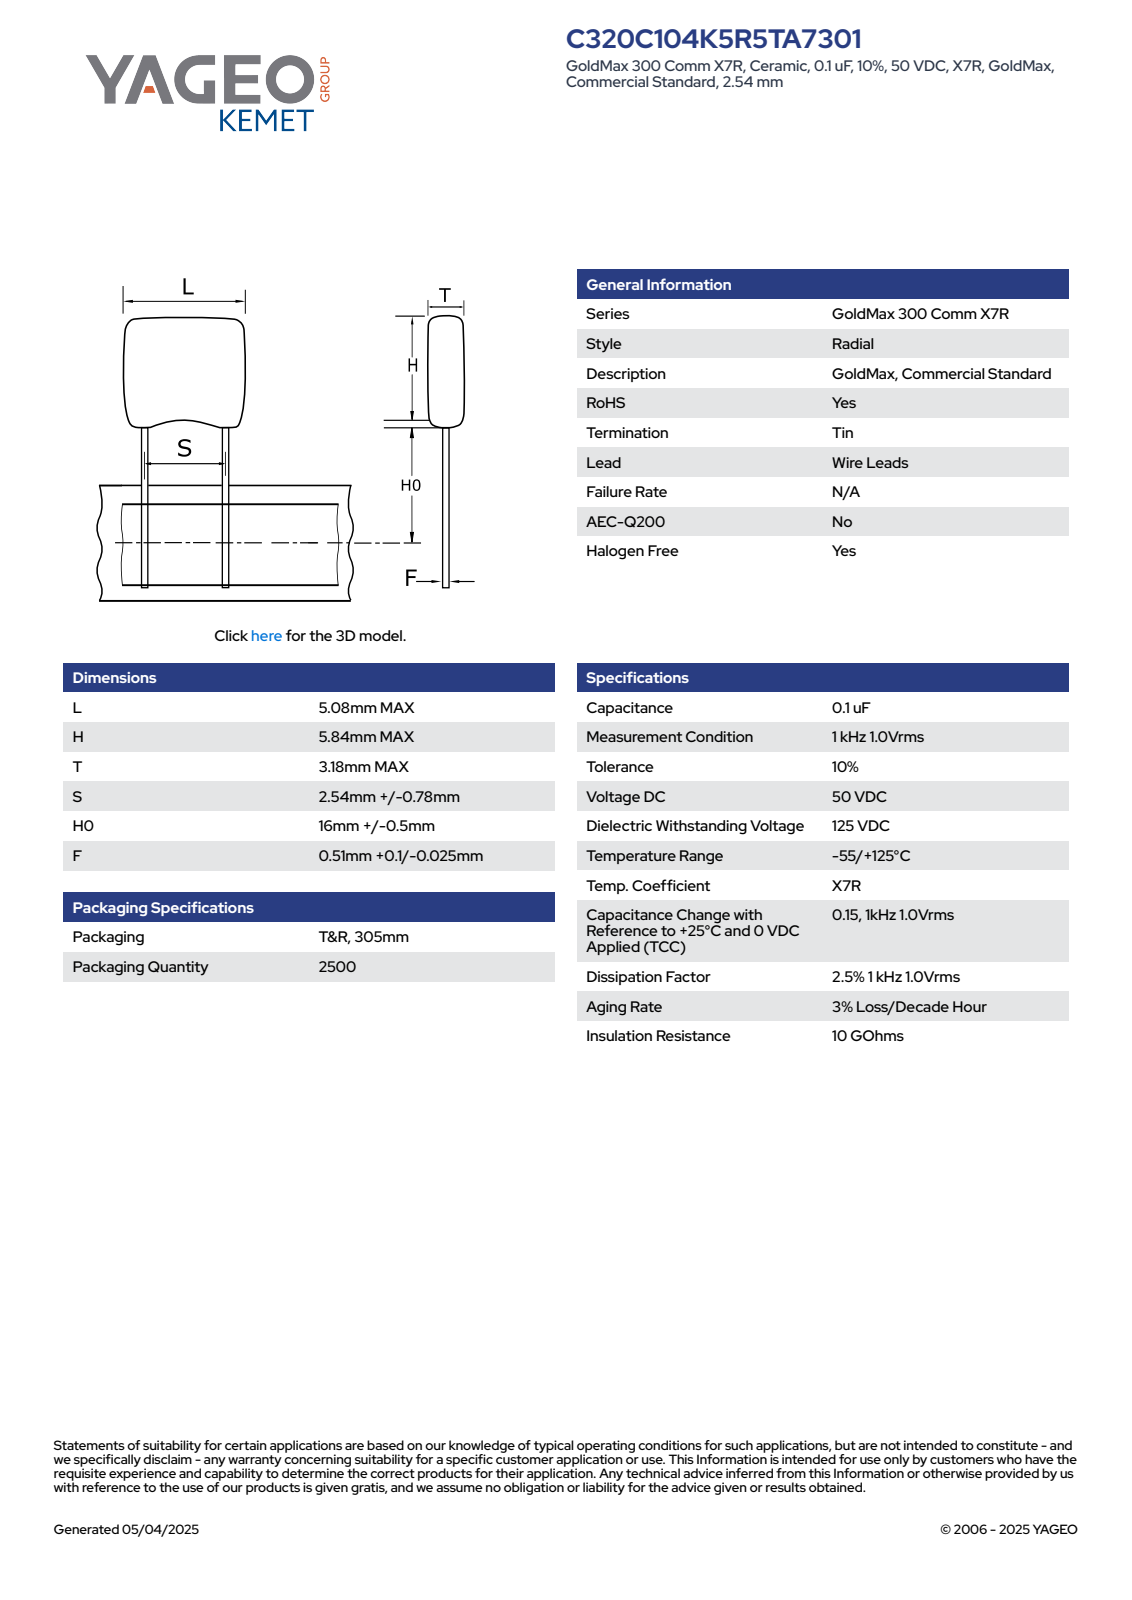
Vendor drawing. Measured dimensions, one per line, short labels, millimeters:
name: CCR_KRCST_5.08X5.84_L5.08H5.84T3.18S2.54H016.5F0.61
written by: SolidWorks 2014 (AUTOMOTIVE_DESIGN)
unit: mm
bodies: 4 solids, 83 faces (65 planar, 14 cylindrical, 4 other)
size: 23.01 × 5.08 × 3.19
volume: 109 mm³; area: 187 mm²
bosses: 2× ⌀0.61
rounds: 10× R0.75
face distances: 3.18, 5.08, 6.51, 16.5, 23.01, 3.19, 0.54, 19.93, 3.43, 3.08
